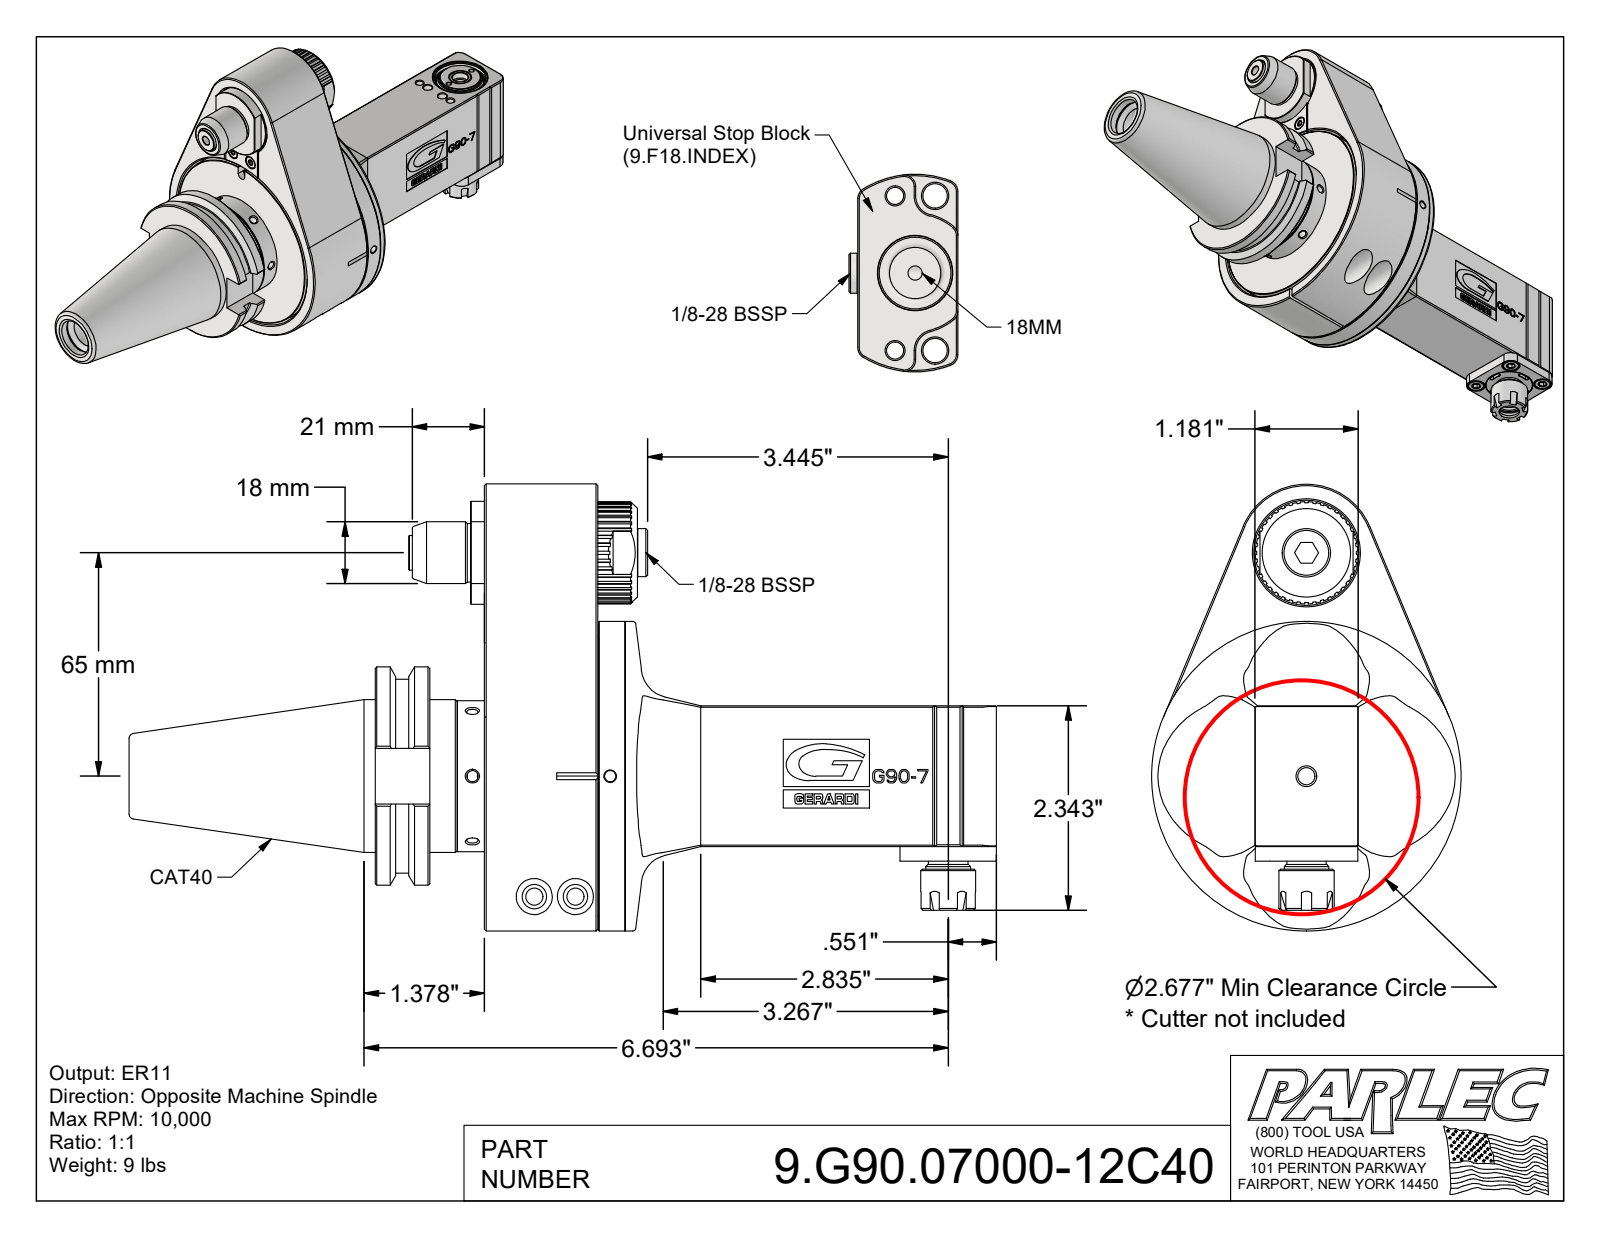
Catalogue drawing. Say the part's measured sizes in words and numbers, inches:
The part is named "9.G90.07000-12C40; G90-7". Its 3-D file was written by "Autodesk Inventor 2022 (AUTOMOTIVE_DESIGN)". It is 3 solids with 1173 faces: 660 planar, 245 cylindrical and 268 other. Overall it measures 9.937 by 5.118 by 3.543 inches. Its volume is 32.8 cubic inches and its surface area 192.2 square inches. Round holes: 7 of diameter 0.13, 5 of diameter 0.197, 5 of diameter 0.295, 4 of diameter 0.157, 4 of diameter 0.165, 3 of diameter 0.276, 2 of diameter 0.083, 2 of diameter 0.236, 2 of diameter 0.413, 1 of diameter 0.217, 1 of diameter 0.24, 1 of diameter 0.335. Round bosses or shafts: 5 of diameter 0.276, 3 of diameter 0.394, 2 of diameter 1.181, 2 of diameter 0.354, 2 of diameter 0.228, 1 of diameter 3.543, 1 of diameter 3.071, 1 of diameter 2.5. Partial cylindrical surfaces (rounded edges, fillets, slot ends): 8 of radius 0.03, 4 of radius 0.167, 4 of radius 0.354, 3 of radius 0.059, 2 of radius 0.079, 2 of radius 0.085, 2 of radius 0.157, 1 of radius 0.115. The main face-to-face distances are 0.118, 1.299, 1.181, 1.173, 0.626, 0.335, 0.217, 0.965, 0.276, 0.039. The hole center spacings are 0.437, 0.571, 0.783, 0.512, 0.551, 0.197, 0.201, 0.231.
